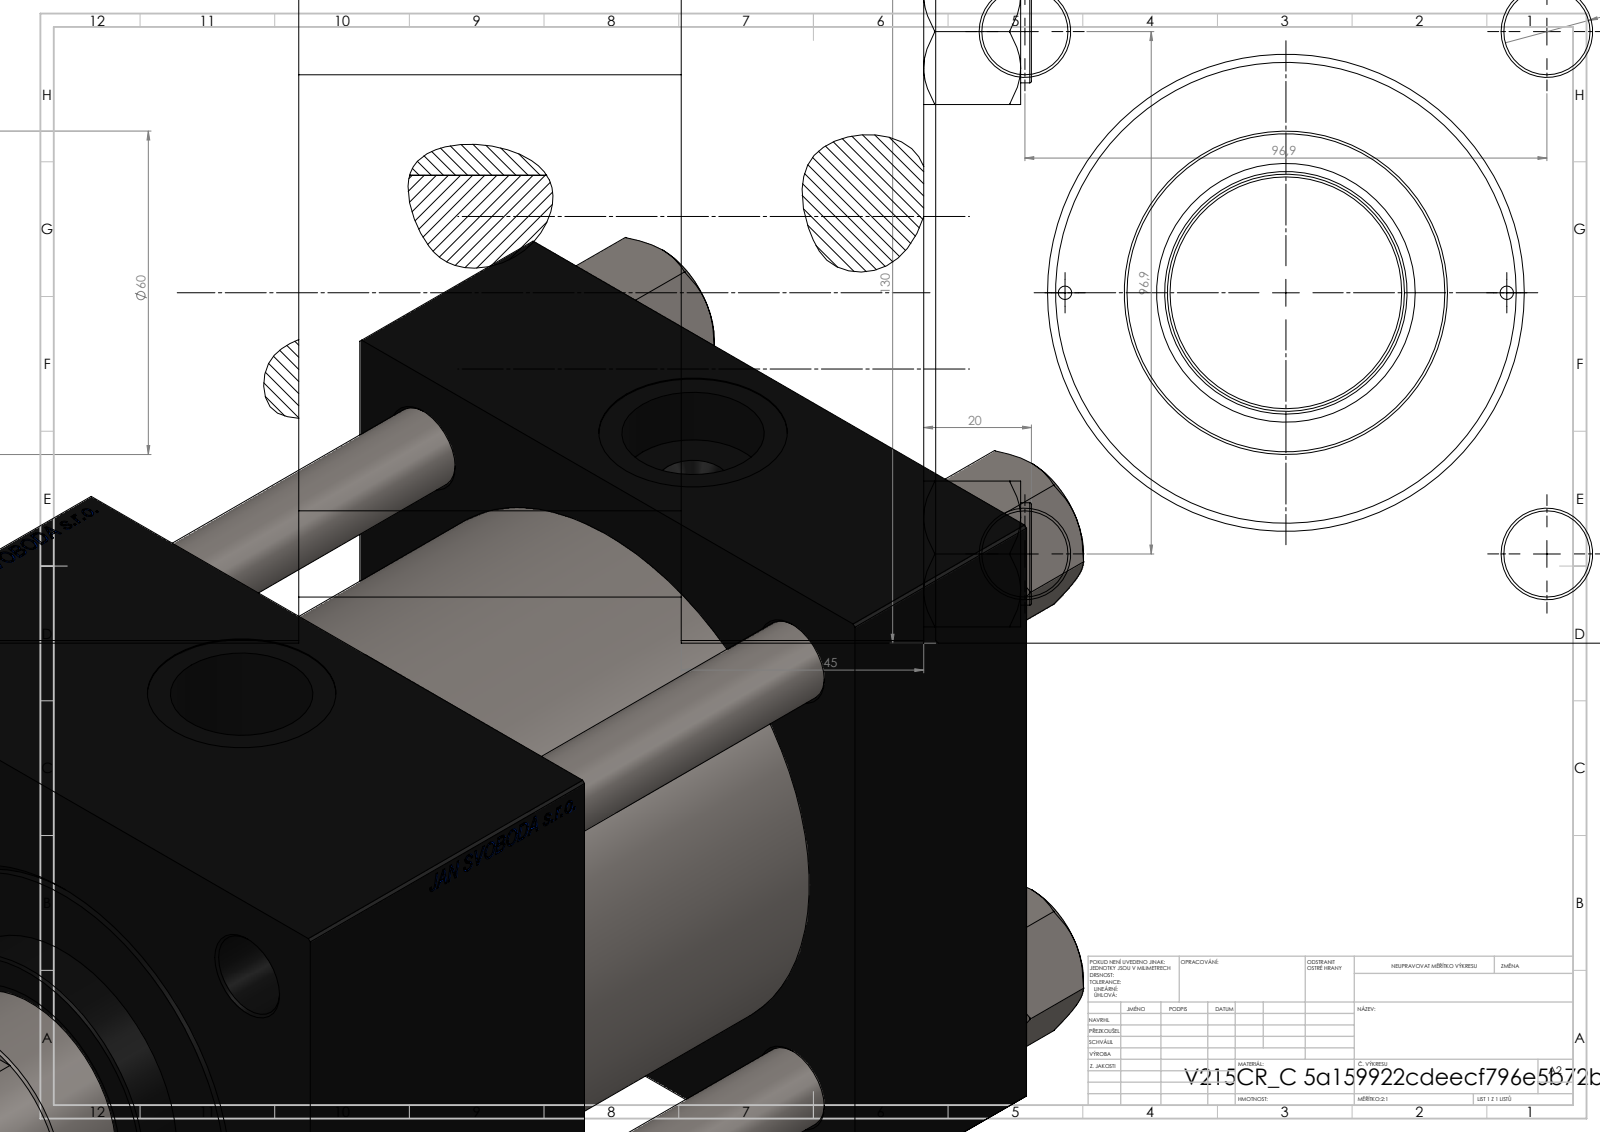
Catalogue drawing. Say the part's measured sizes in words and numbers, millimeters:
The part is named "V215CR_ROD_END_F; V215CR_VCP_C; V215_VC_A; V215CR_C_TYCINKA (+2 more)". Its 3-D file was written by "SolidWorks 2019 (CONFIG_CONTROL_DESIGN)". It is 12 solids with 1216 faces: 579 planar, 95 cylindrical and 542 other. Overall it measures 287 by 130 by 130 millimeters. Its volume is 2 477 000 cubic millimeters and its surface area 334 853 square millimeters. Round holes: 4 of diameter 16, 2 of diameter 2.5, 2 of diameter 7, 2 of diameter 26.44, 2 of diameter 35, 1 of diameter 31.5, 1 of diameter 45, 1 of diameter 48, 1 of diameter 76, 1 of diameter 85.5, 1 of diameter 100. Round bosses or shafts: 4 of diameter 19, 1 of diameter 106, 1 of diameter 60, 1 of diameter 44, 1 of diameter 33. The main face-to-face distances are 130, 45, 188, 143, 116, 71, 72, 20, 96, 51. The hole center spacings are 49.02, 68.52, 96.9, 101.73, 41, 137.04, 82, 118.5.
